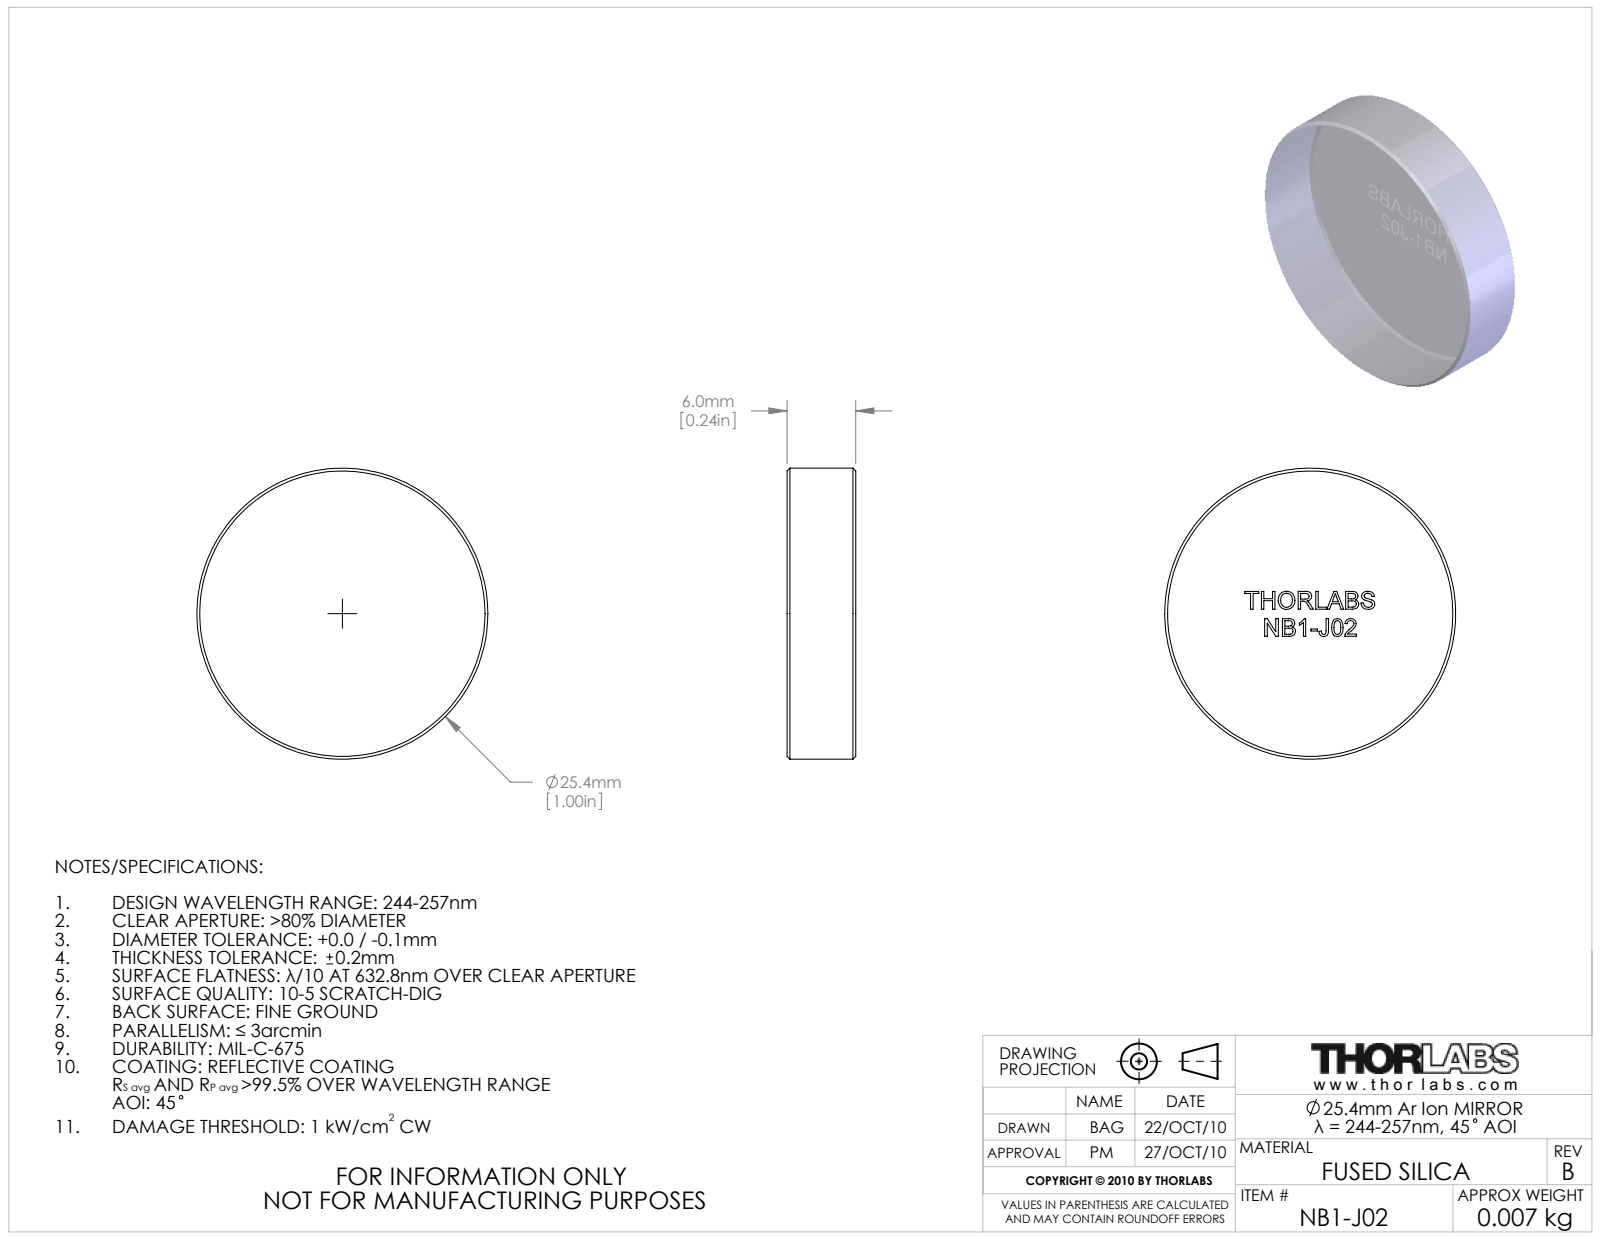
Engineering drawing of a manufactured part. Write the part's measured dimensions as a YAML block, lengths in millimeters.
part_name: "8774-E0W"
step_written_by: "SolidWorks 2009 (AUTOMOTIVE_DESIGN)"
units: millimeters
bodies: {solids: 1, faces: 203, planar: 120, cylindrical: 2, other: 81}
overall_size: [25.4, 25.4, 6]
volume: 3030
surface_area: 1468
round_bosses_or_shafts:
  - {diameter: 25.4, count: 1}
face_to_face_distances: [6, 1.5, 2.4, 2.4, 2.9, 1.9, 4.1, 1, 4.4, 0.9]
